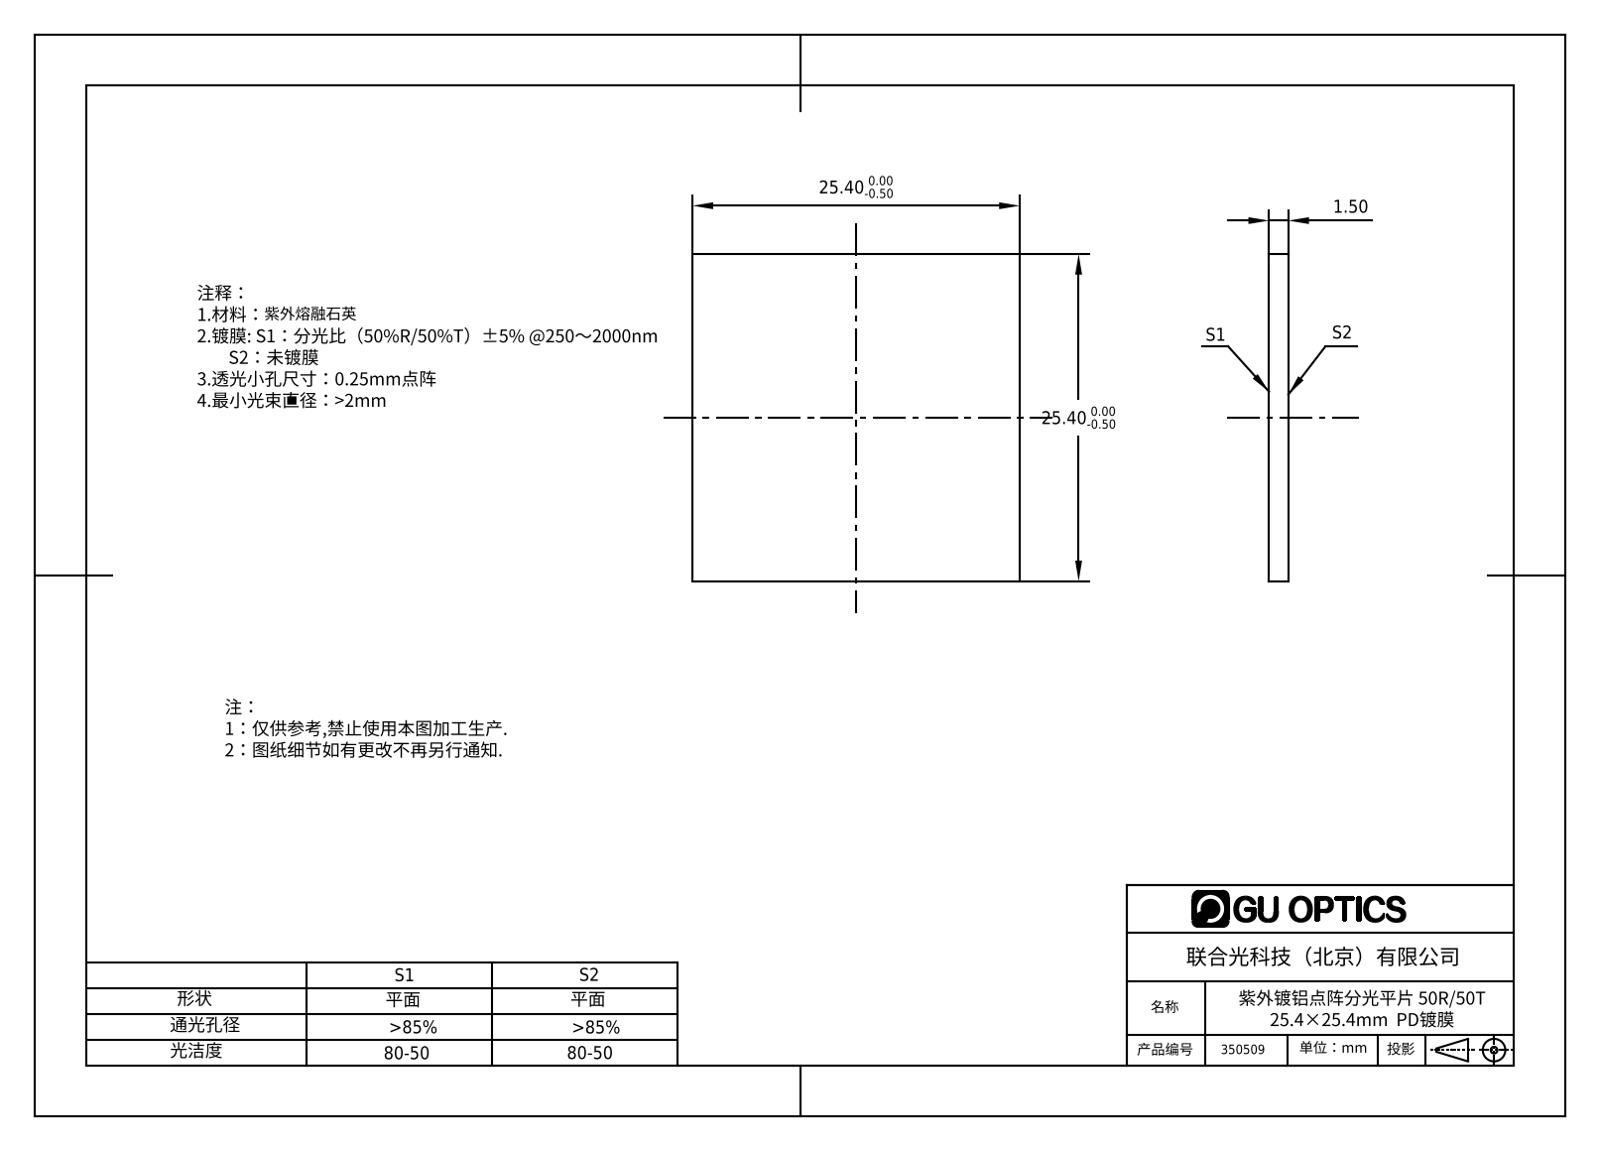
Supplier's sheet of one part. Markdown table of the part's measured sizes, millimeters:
| quantity | value |
| --- | --- |
| part name | 350503 |
| STEP written by | SolidWorks 2016 (AUTOMOTIVE_DESIGN) |
| units | millimeters |
| bodies | 1 solid, 6 faces (6 planar, 0 cylindrical, 0 other) |
| overall size | 25.4 × 25.4 × 1.5 |
| volume | 968 mm³ |
| surface area | 1 443 mm² |
| main face-to-face distances | 1.5, 25.4 |
